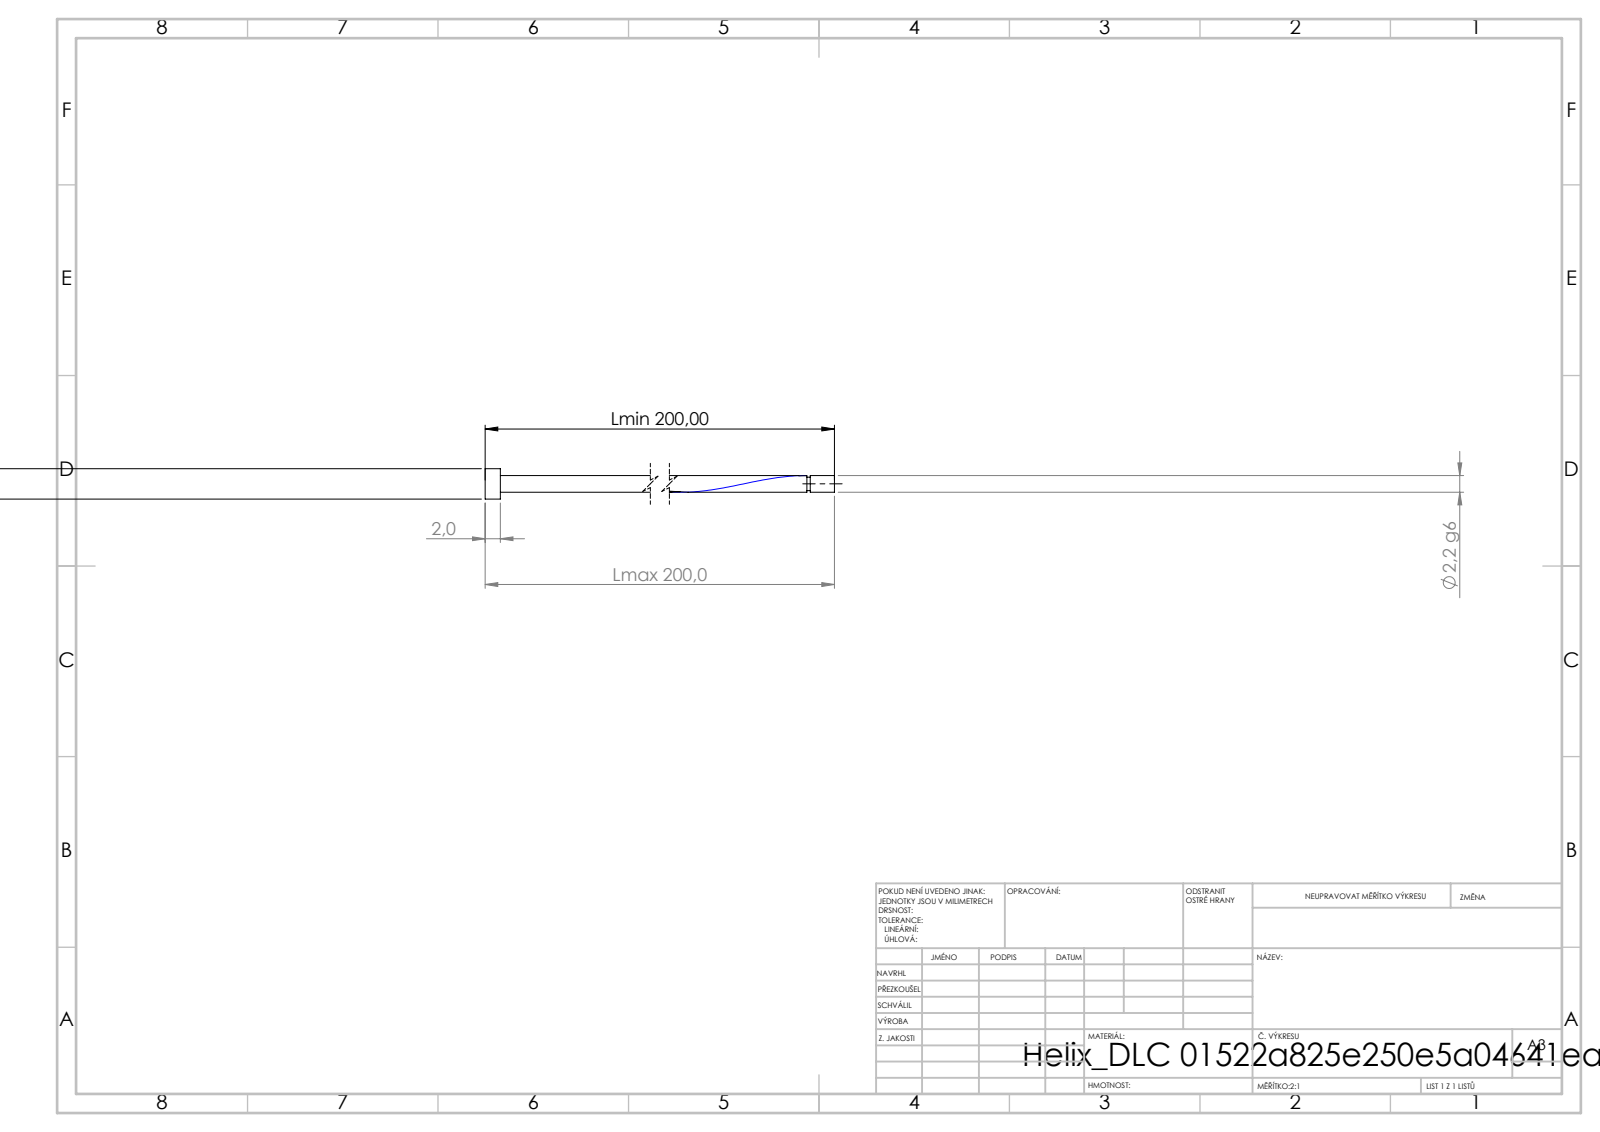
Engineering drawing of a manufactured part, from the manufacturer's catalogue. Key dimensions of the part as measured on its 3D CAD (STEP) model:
STEP written by: SolidWorks 2019 (CONFIG_CONTROL_DESIGN)
Units: millimetres
Bodies: 1 solid, 16 faces (6 planar, 9 cylindrical, 1 other)
Overall size (bounding box): 200 × 4 × 4
Volume: 939 mm³ · Surface area: 1 903 mm²
Round bosses / shafts (diameter × count): ⌀4 ×1, ⌀2.2 ×1, ⌀1.76 ×1
Main face-to-face distances: 2, 200, 198, 196.83, 194.83, 3.17, 196.39, 194.39, 0.44, 3.61
